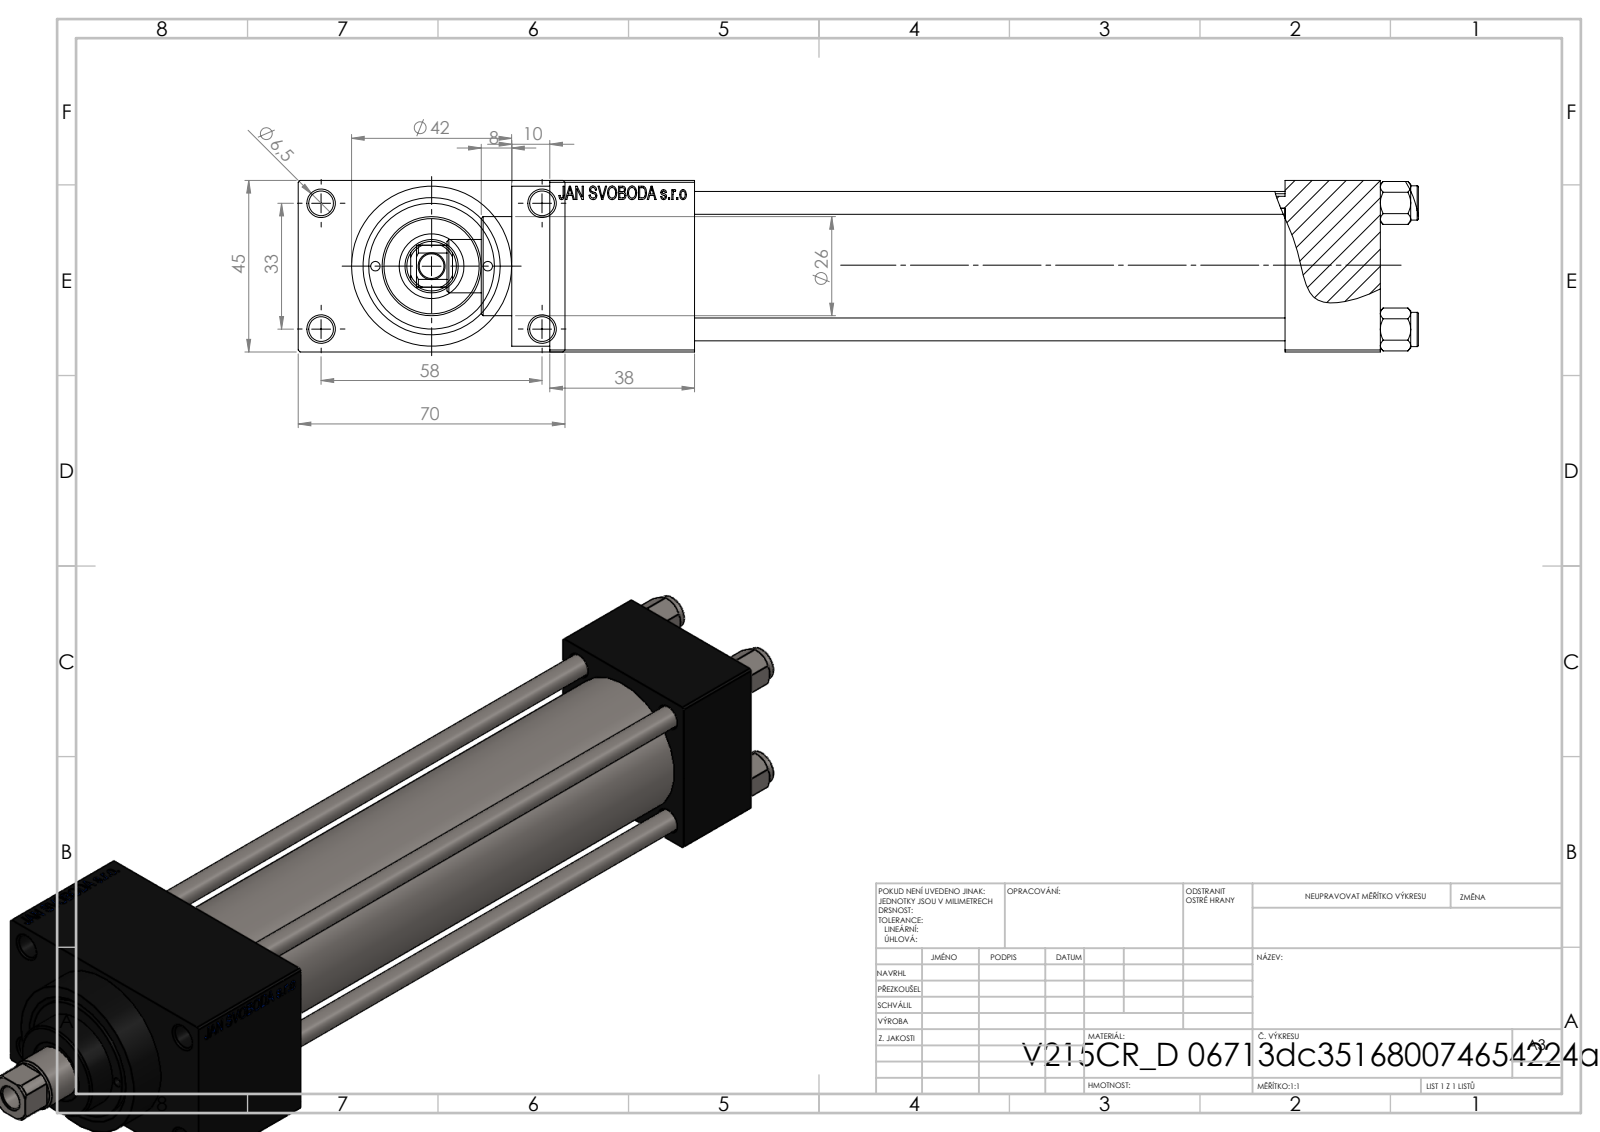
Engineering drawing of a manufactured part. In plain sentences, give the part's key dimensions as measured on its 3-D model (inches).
The part is named "NUT_M5_D; V215CR_D_Body; V215CR_D_TYCINKA; V215CR_VCP_D (+1 more)". Its 3-D file was written by "SolidWorks 2019 (CONFIG_CONTROL_DESIGN)". It is 11 solids with 1110 faces: 498 planar, 92 cylindrical and 520 other. Overall it measures 10.354 by 2.756 by 1.772 inches. Its volume is 17.87 cubic inches and its surface area 172.1 square inches. Round holes: 5 of diameter 0.256, 4 of diameter 0.236, 2 of diameter 0.098, 2 of diameter 0.276, 2 of diameter 0.518, 2 of diameter 0.787, 1 of diameter 0.551, 1 of diameter 0.669, 1 of diameter 0.945, 1 of diameter 1.26, 1 of diameter 1.299. Round bosses or shafts: 4 of diameter 0.354, 1 of diameter 1.654, 1 of diameter 1.496, 1 of diameter 1.024. Partial cylindrical surfaces (rounded edges, fillets, slot ends): 1 of radius 0.256. The main face-to-face distances are 1.772, 0.984, 0.492, 6.102, 7.087, 2.264, 7.598, 1.496, 8.583, 2.756. The hole center spacings are 0.488, 0.657, 0.858, 0.924, 1.307, 1.314, 1.392, 1.396.
